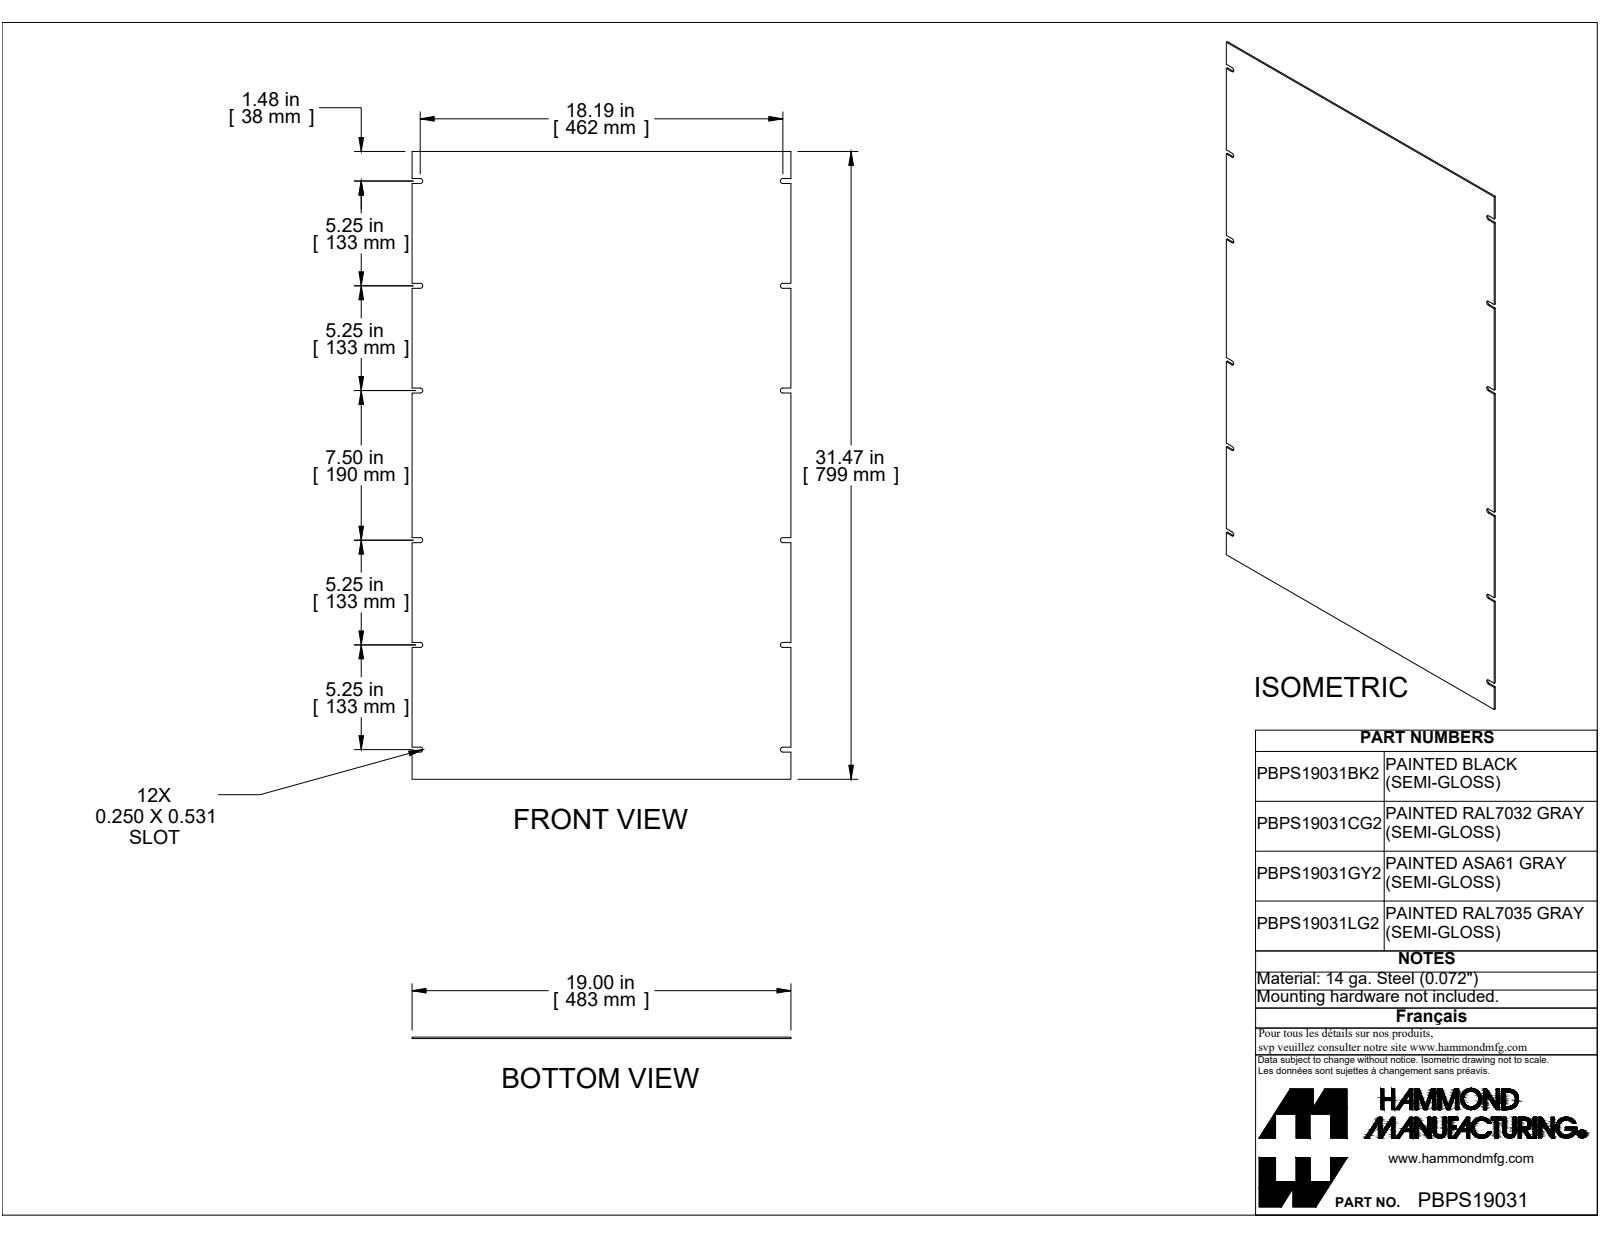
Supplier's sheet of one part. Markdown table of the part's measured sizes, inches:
| quantity | value |
| --- | --- |
| part name | PBPS19031LG2 |
| STEP written by | SolidWorks 2019 (CONFIG_CONTROL_DESIGN) |
| units | inches |
| bodies | 1 solid, 54 faces (42 planar, 12 cylindrical, 0 other) |
| overall size | 31.468 × 19 × 0.072 |
| volume | 42.94 in³ |
| surface area | 1 201 in² |
| partial cylindrical surfaces (radius × count) | 0.125 × 12 |
| main face-to-face distances | 0.072, 19, 31.468, 5.25, 18, 0.25, 5.5, 5.25, 0.25, 12.75 |
